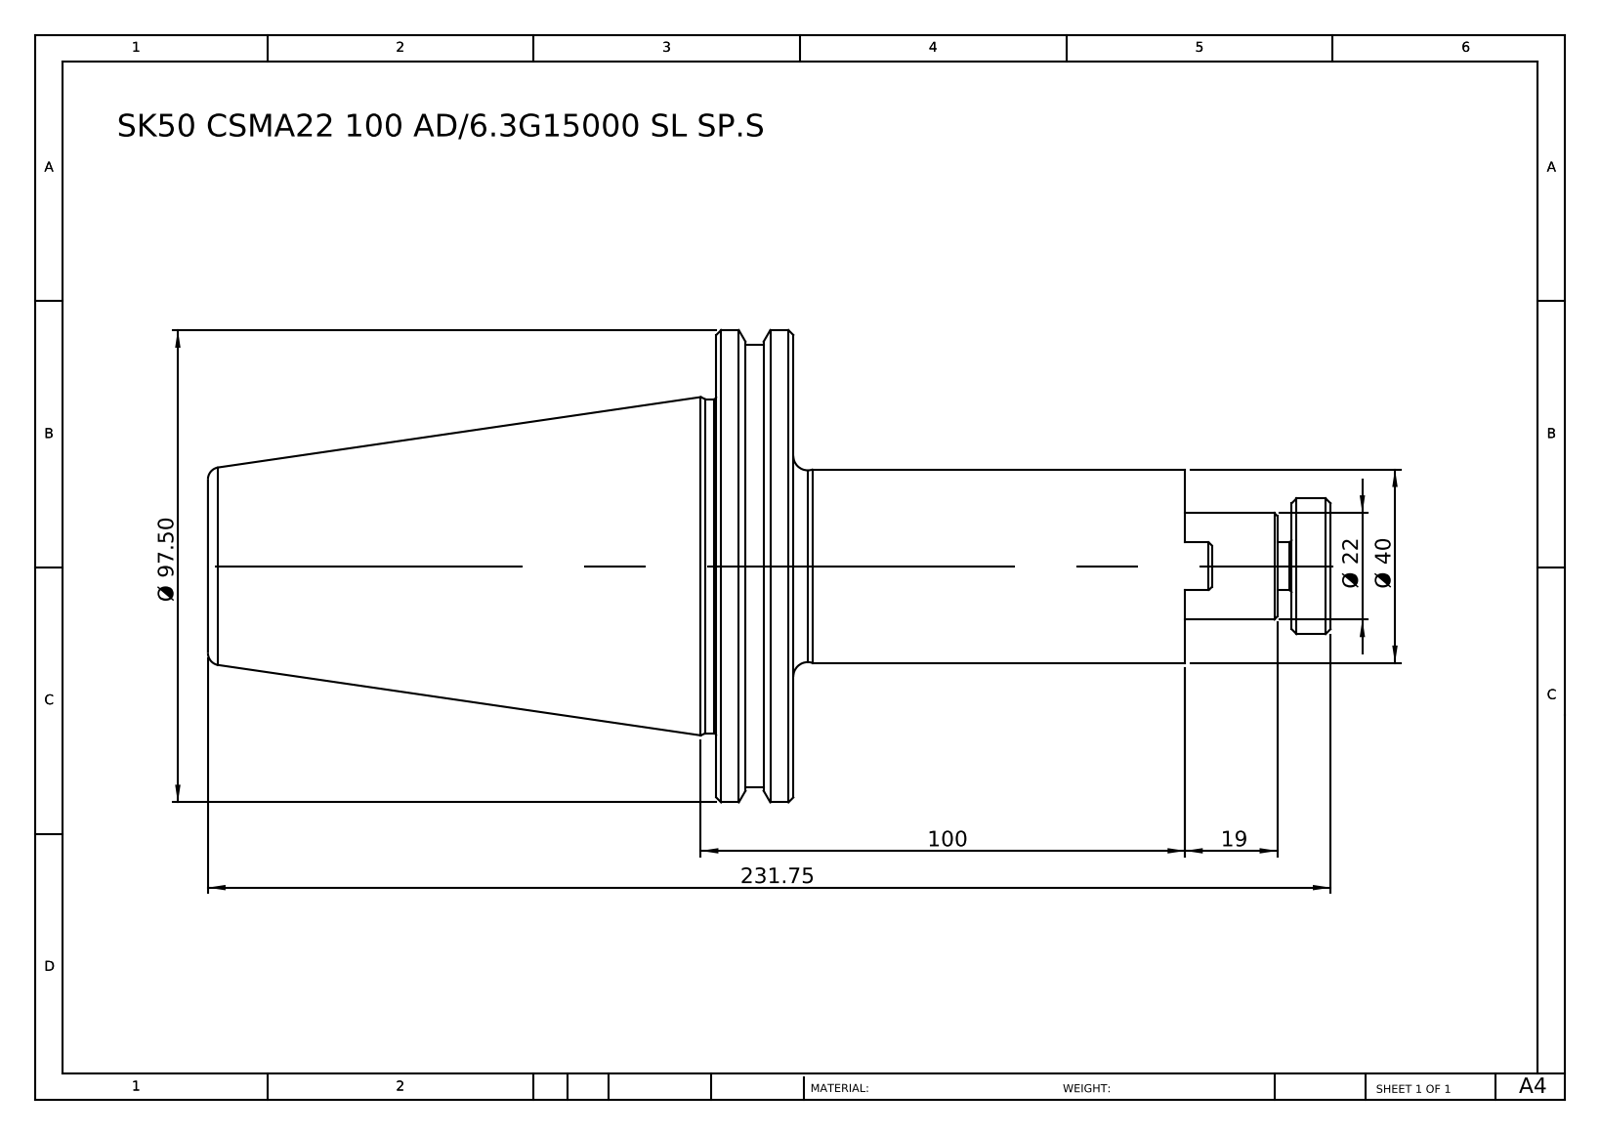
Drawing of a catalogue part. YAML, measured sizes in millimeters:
part_name: "SK 50 CSMA22 100 AD-6.3G15000 SL SP.S"
step_written_by: "SolidWorks 2014 (CONFIG_CONTROL_DESIGN)"
units: millimeters
bodies: {solids: 1, faces: 76, planar: 23, cylindrical: 21, other: 32}
overall_size: [231.75, 97.5, 97.5]
volume: 488634
surface_area: 49944
round_bosses_or_shafts:
  - {diameter: 97.5, count: 1}
  - {diameter: 91.3, count: 1}
  - {diameter: 69, count: 1}
  - {diameter: 40, count: 1}
  - {diameter: 28, count: 1}
  - {diameter: 22, count: 1}
  - {diameter: 10, count: 1}
partial_cylinders:
  - {radius: 3, count: 1}
  - {radius: 13, count: 1}
face_to_face_distances: [15.9, 120.85, 104.95, 80.9, 96.8, 201.75, 30, 110.9, 126.8, 231.75]
